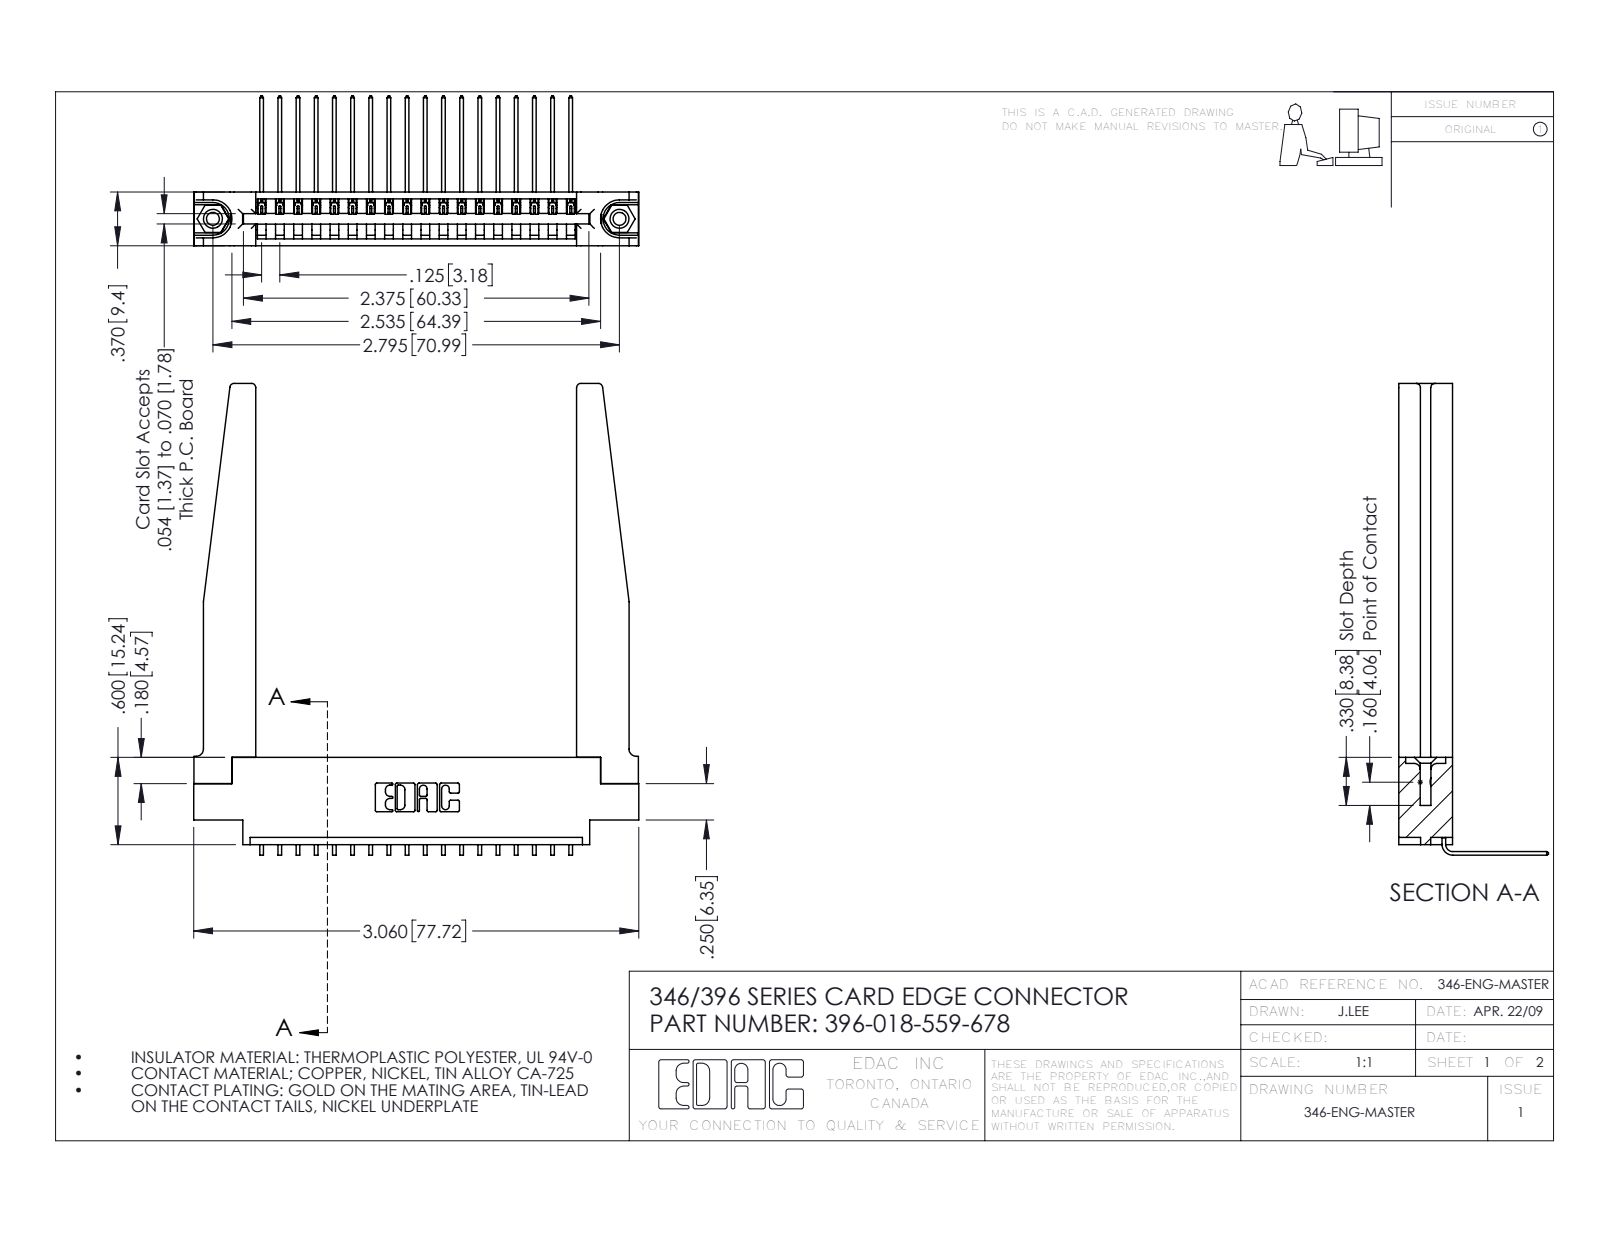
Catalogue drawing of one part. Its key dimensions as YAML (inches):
part_name: "396-018-559-678; 346 Part_0.170 Offset - 0.156 Dia-TH; 345-292-001_558 559 Tail - 1; 346-220-078_345-220-078 (+1 more)"
step_written_by: "SolidWorks 2016 (CONFIG_CONTROL_DESIGN)"
units: inches
bodies: {solids: 23, faces: 1440, planar: 978, cylindrical: 410, other: 52}
overall_size: [3.243, 3.06, 1.03]
volume: 0.86
surface_area: 24.45
round_holes:
  - {diameter: 0.089, count: 2}
  - {diameter: 0.125, count: 2}
  - {diameter: 0.156, count: 2}
  - {diameter: 0.064, count: 1}
round_bosses_or_shafts:
  - {diameter: 0.155, count: 2}
partial_cylinders:
  - {radius: 0.006, count: 36}
  - {radius: 0.01, count: 22}
  - {radius: 0.03, count: 8}
  - {radius: 0.007, count: 6}
  - {radius: 0.031, count: 6}
  - {radius: 0.026, count: 3}
  - {radius: 0.05, count: 3}
  - {radius: 0.031, count: 2}
face_to_face_distances: [0.37, 0.072, 0.048, 0.15, 0.148, 0.322, 0.25, 0.025, 0.102, 0.22]
hole_center_spacings: [0.246, 2.588, 2.795]
